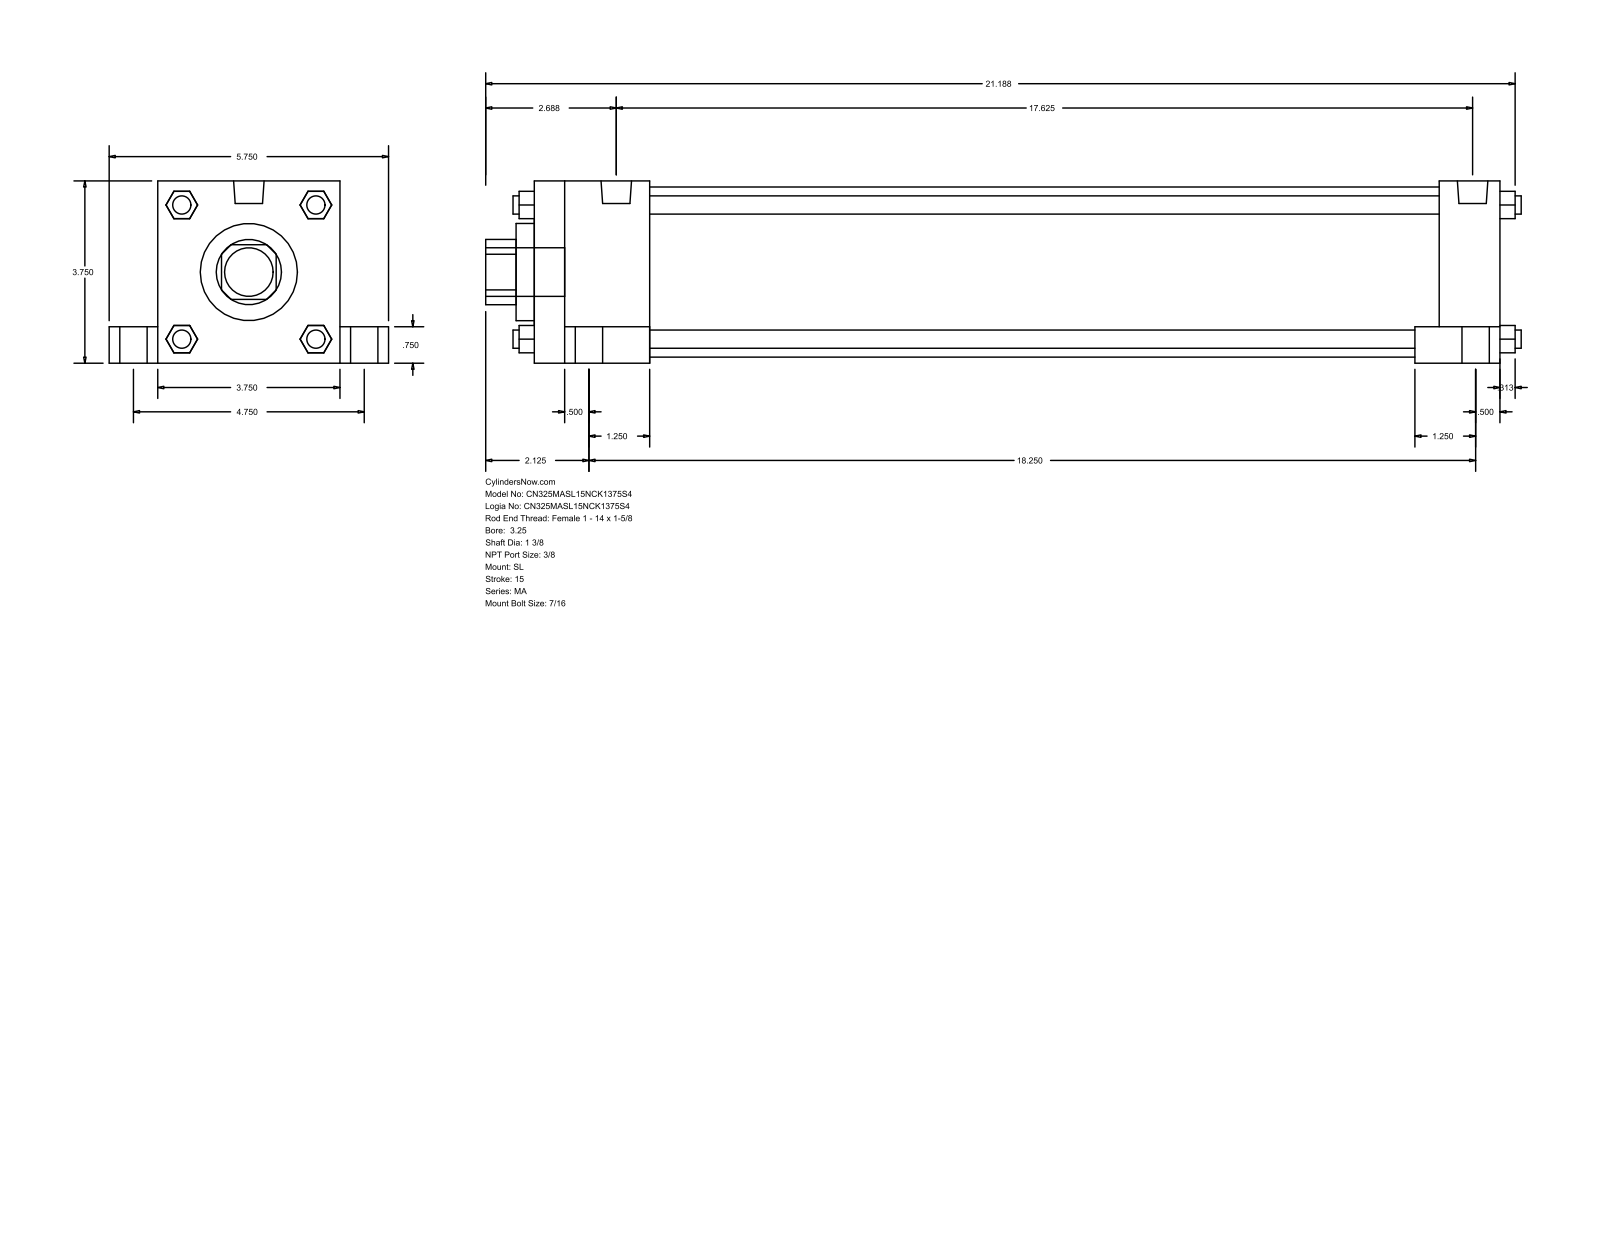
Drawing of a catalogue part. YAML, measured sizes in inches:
part_name: "MA_SL__0325_1.375"
step_written_by: "GSSL Pune (CONFIG_CONTROL_DESIGN)"
units: inches
bodies: {solids: 0, faces: 148, planar: 112, cylindrical: 36, other: 0}
overall_size: [21.313, 5.75, 3.75]
round_holes:
  - {diameter: 1.375, count: 1}
  - {diameter: 2, count: 1}
  - {diameter: 3.5, count: 1}
round_bosses_or_shafts:
  - {diameter: 0.813, count: 4}
  - {diameter: 0.563, count: 4}
  - {diameter: 0.437, count: 4}
  - {diameter: 0.375, count: 4}
  - {diameter: 0.627, count: 2}
  - {diameter: 1, count: 1}
partial_cylinders:
  - {radius: 0.672, count: 1}
face_to_face_distances: [3.75, 19.875, 1, 4.75, 18.625, 1.25, 2.375, 16.25, 17.5, 0.75]
